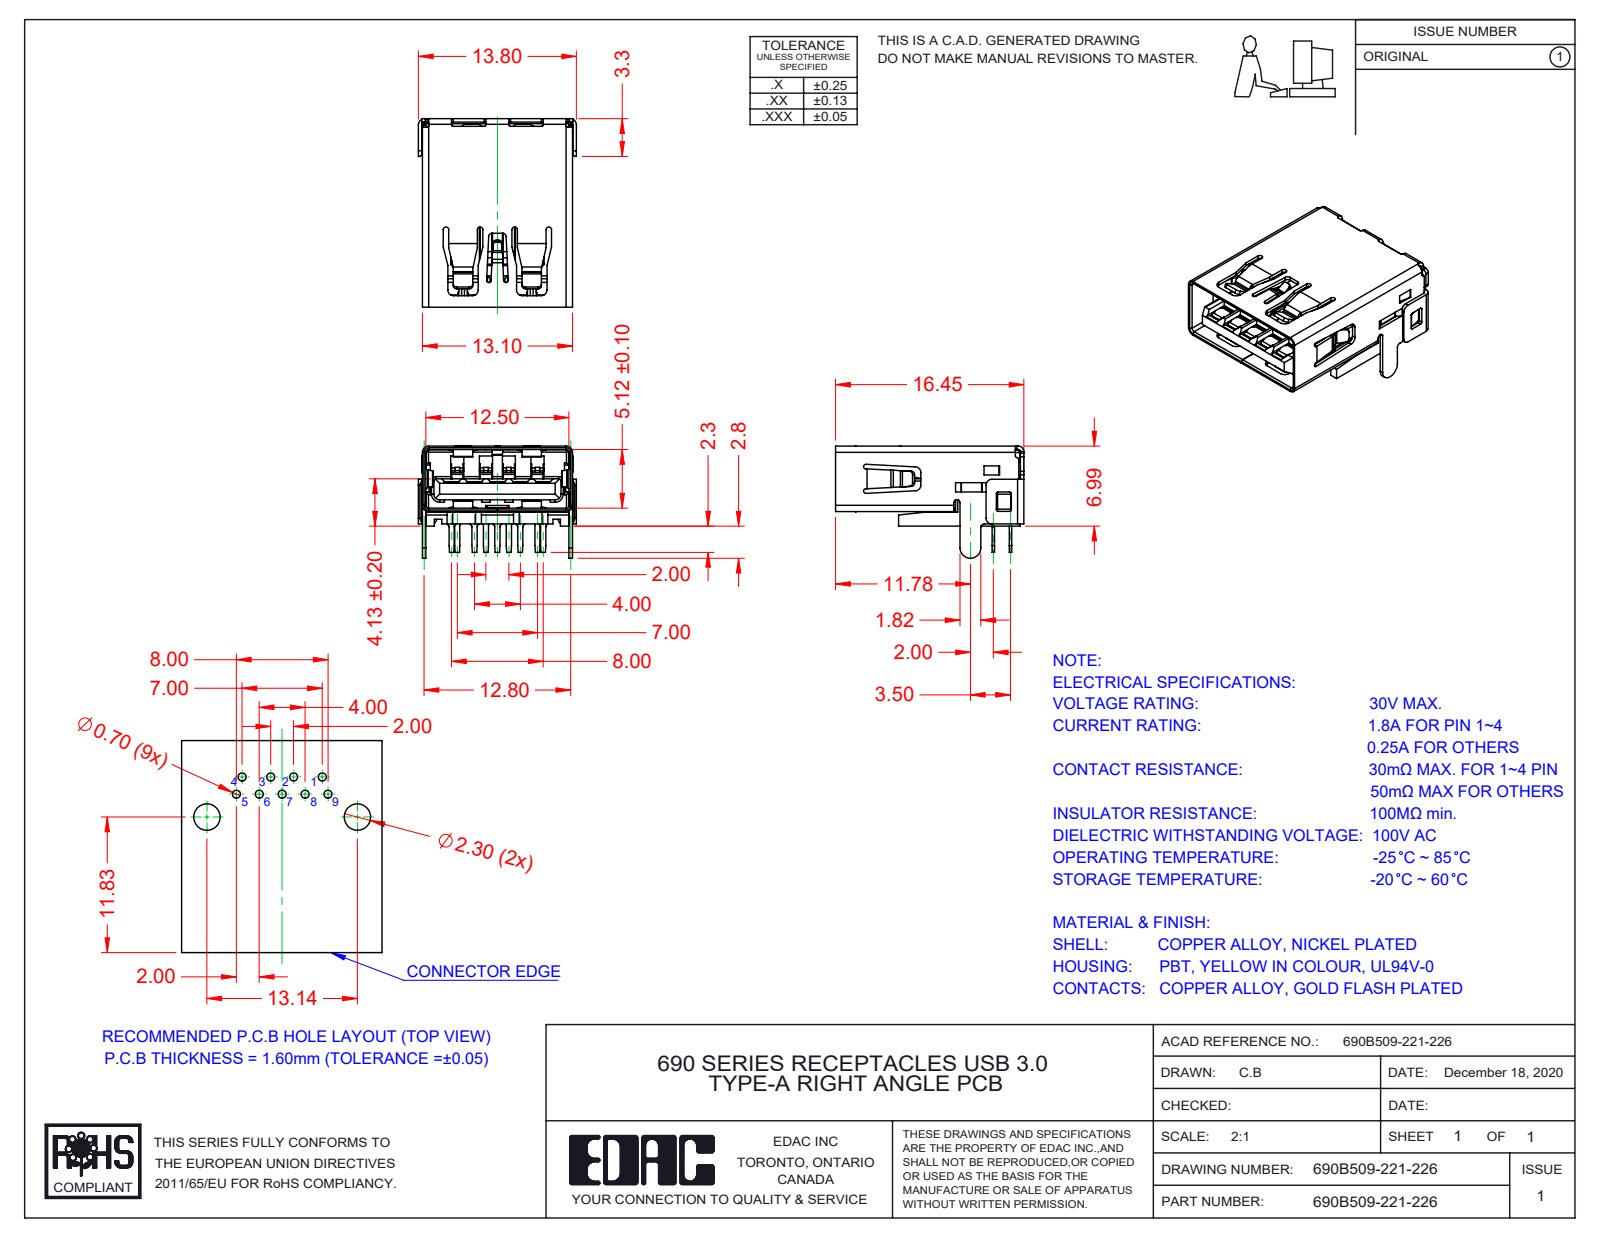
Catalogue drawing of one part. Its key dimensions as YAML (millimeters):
part_name: "Contact 2.0 690B509-221-226; Contact 3.0 690B509-221-226; Shell 690B509-221-226; 690B509-221-226 (+4 more)"
step_written_by: "SolidWorks 2020 (AUTOMOTIVE_DESIGN)"
units: millimeters
bodies: {solids: 12, faces: 2409, planar: 1582, cylindrical: 705, other: 122}
overall_size: [16.45, 13.8, 9.82]
volume: 666
surface_area: 3052
partial_cylinders:
  - {radius: 0.15, count: 154}
  - {radius: 0.2, count: 67}
  - {radius: 0.3, count: 61}
  - {radius: 0.1, count: 24}
  - {radius: 0.13, count: 20}
  - {radius: 0.5, count: 20}
  - {radius: 0.45, count: 10}
  - {radius: 0.25, count: 9}
face_to_face_distances: [5.42, 2.56, 1.02, 12.8, 0.35, 1.07, 2.86, 2.91, 0.72, 3.58]
